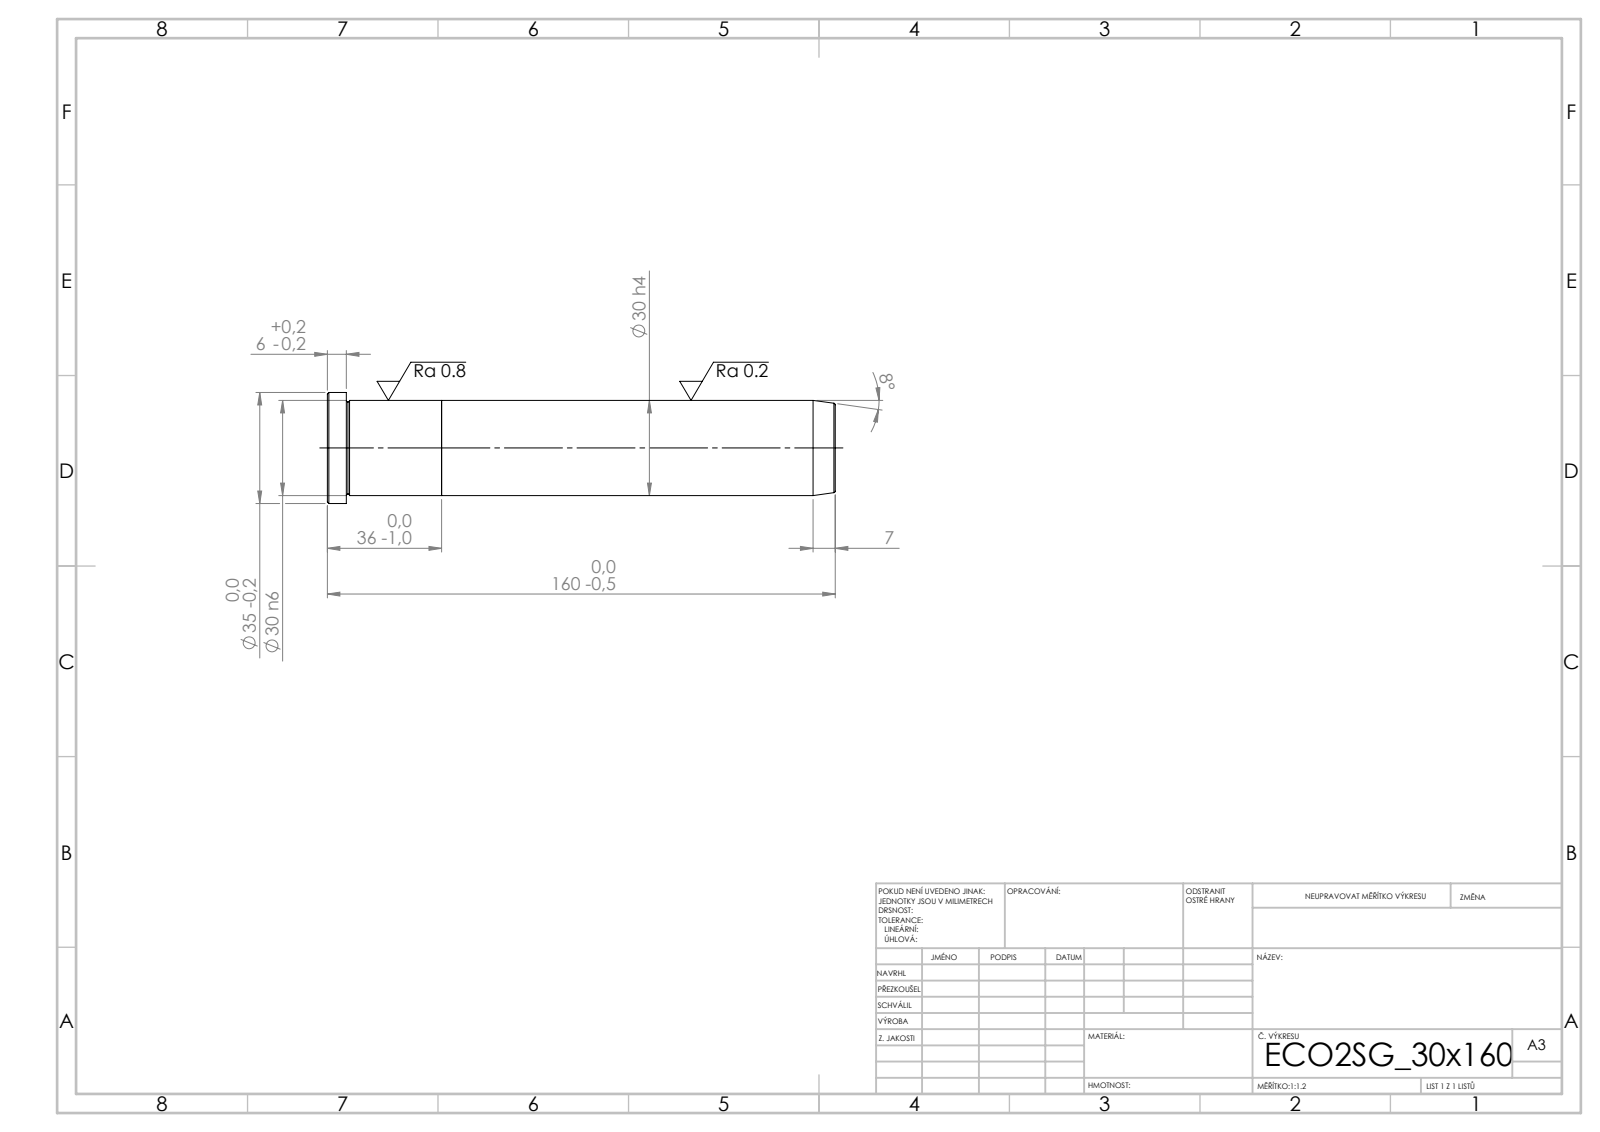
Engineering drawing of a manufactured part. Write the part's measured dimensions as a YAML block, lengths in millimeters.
step_written_by: "SolidWorks 2019 (CONFIG_CONTROL_DESIGN)"
units: millimeters
bodies: {solids: 2, faces: 21, planar: 5, cylindrical: 6, other: 10}
overall_size: [160, 35, 35]
volume: 114258
surface_area: 18411
round_bosses_or_shafts:
  - {diameter: 35, count: 1}
  - {diameter: 30, count: 1}
face_to_face_distances: [36, 124, 160, 154, 30, 6]
